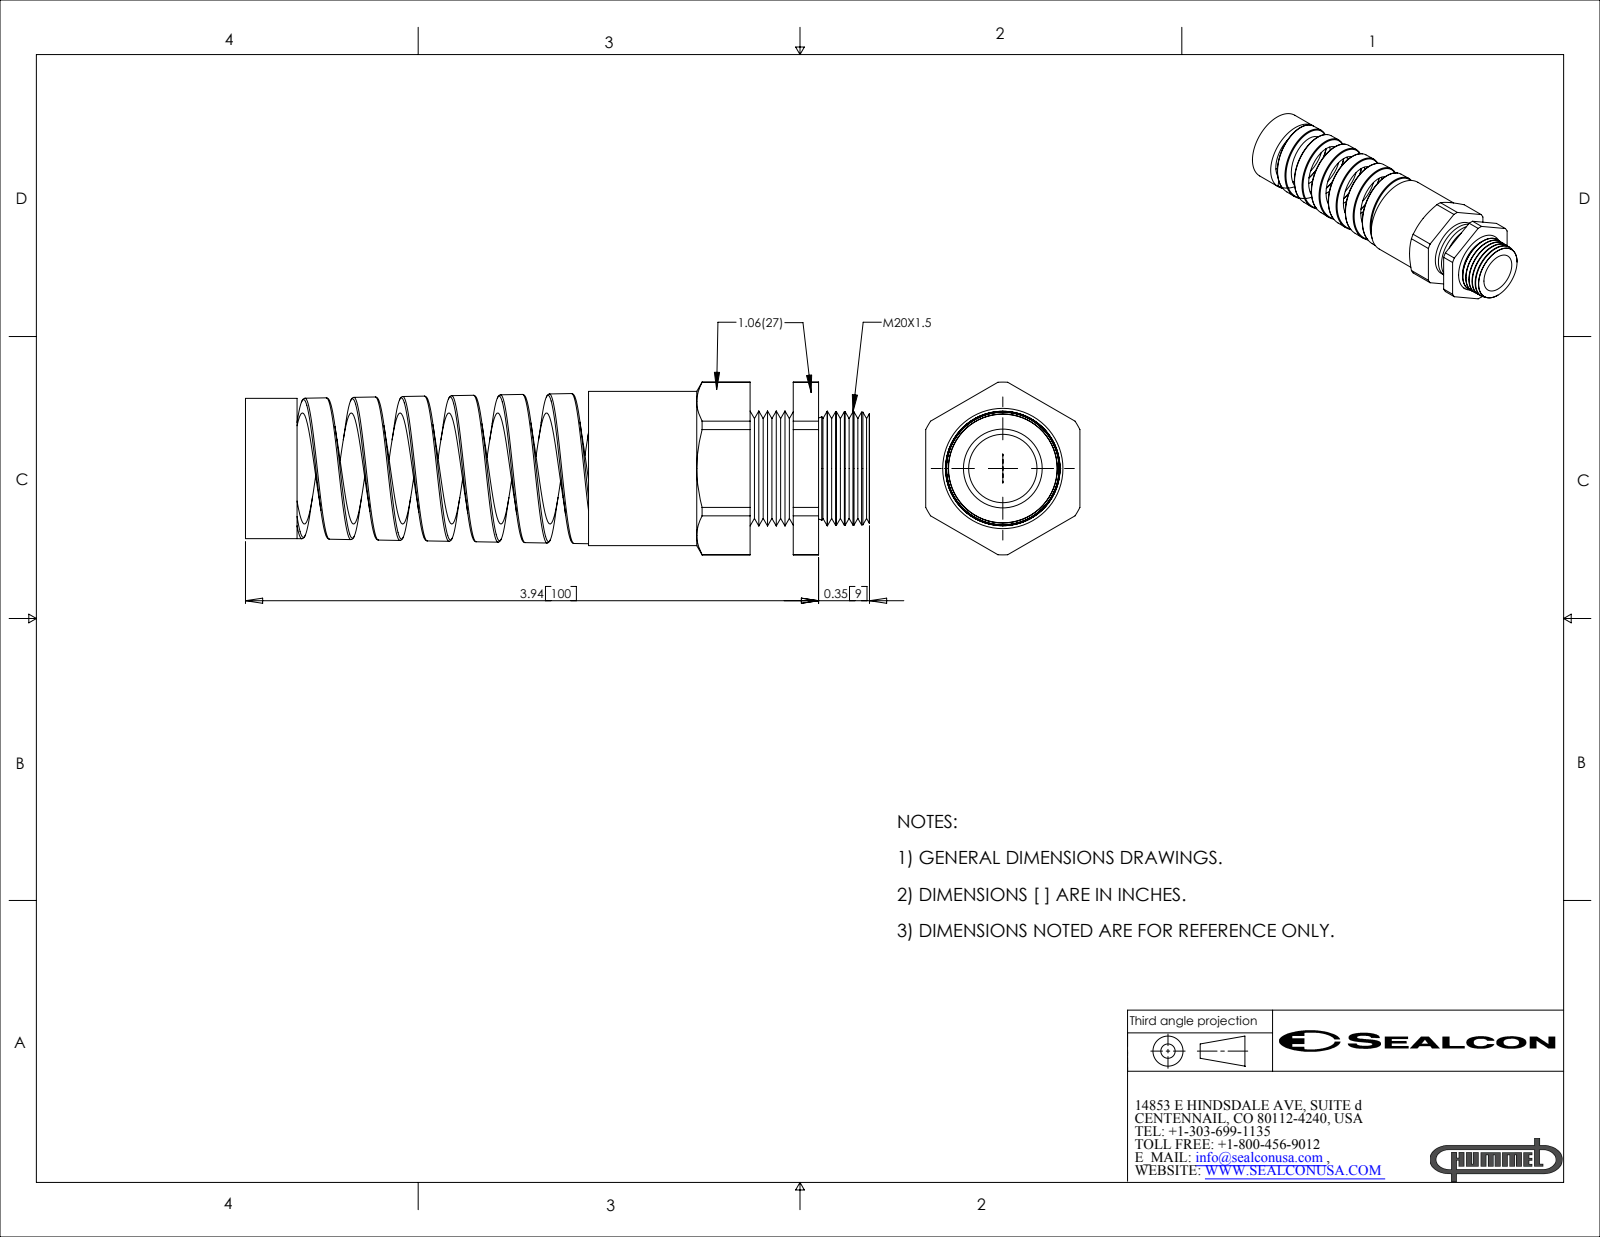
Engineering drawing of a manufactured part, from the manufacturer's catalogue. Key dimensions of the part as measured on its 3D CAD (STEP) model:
Part name (STEP PRODUCT): CF22MR-GY
STEP written by: SolidWorks 2007 (CONFIG_CONTROL_DESIGN)
Units: inches
Bodies: 1 solid, 139 faces (19 planar, 34 cylindrical, 86 other)
Overall size (bounding box): 4.29 × 1.187 × 1.06
Volume: 1.533 in³ · Surface area: 24.6 in²
Round holes (diameter × count): ⌀0.47 ×1, ⌀0.764 ×1, ⌀0.79 ×1
Round bosses / shafts (diameter × count): ⌀1.06 ×1, ⌀0.964 ×1
Partial cylindrical surfaces — rounded edges, fillets, slot ends (radius × count): R0.594 ×1
Main face-to-face distances: 1.06, 1.111, 1.407, 0.297, 1.581, 0.471, 0.174, 2.359, 3.469, 3.766
